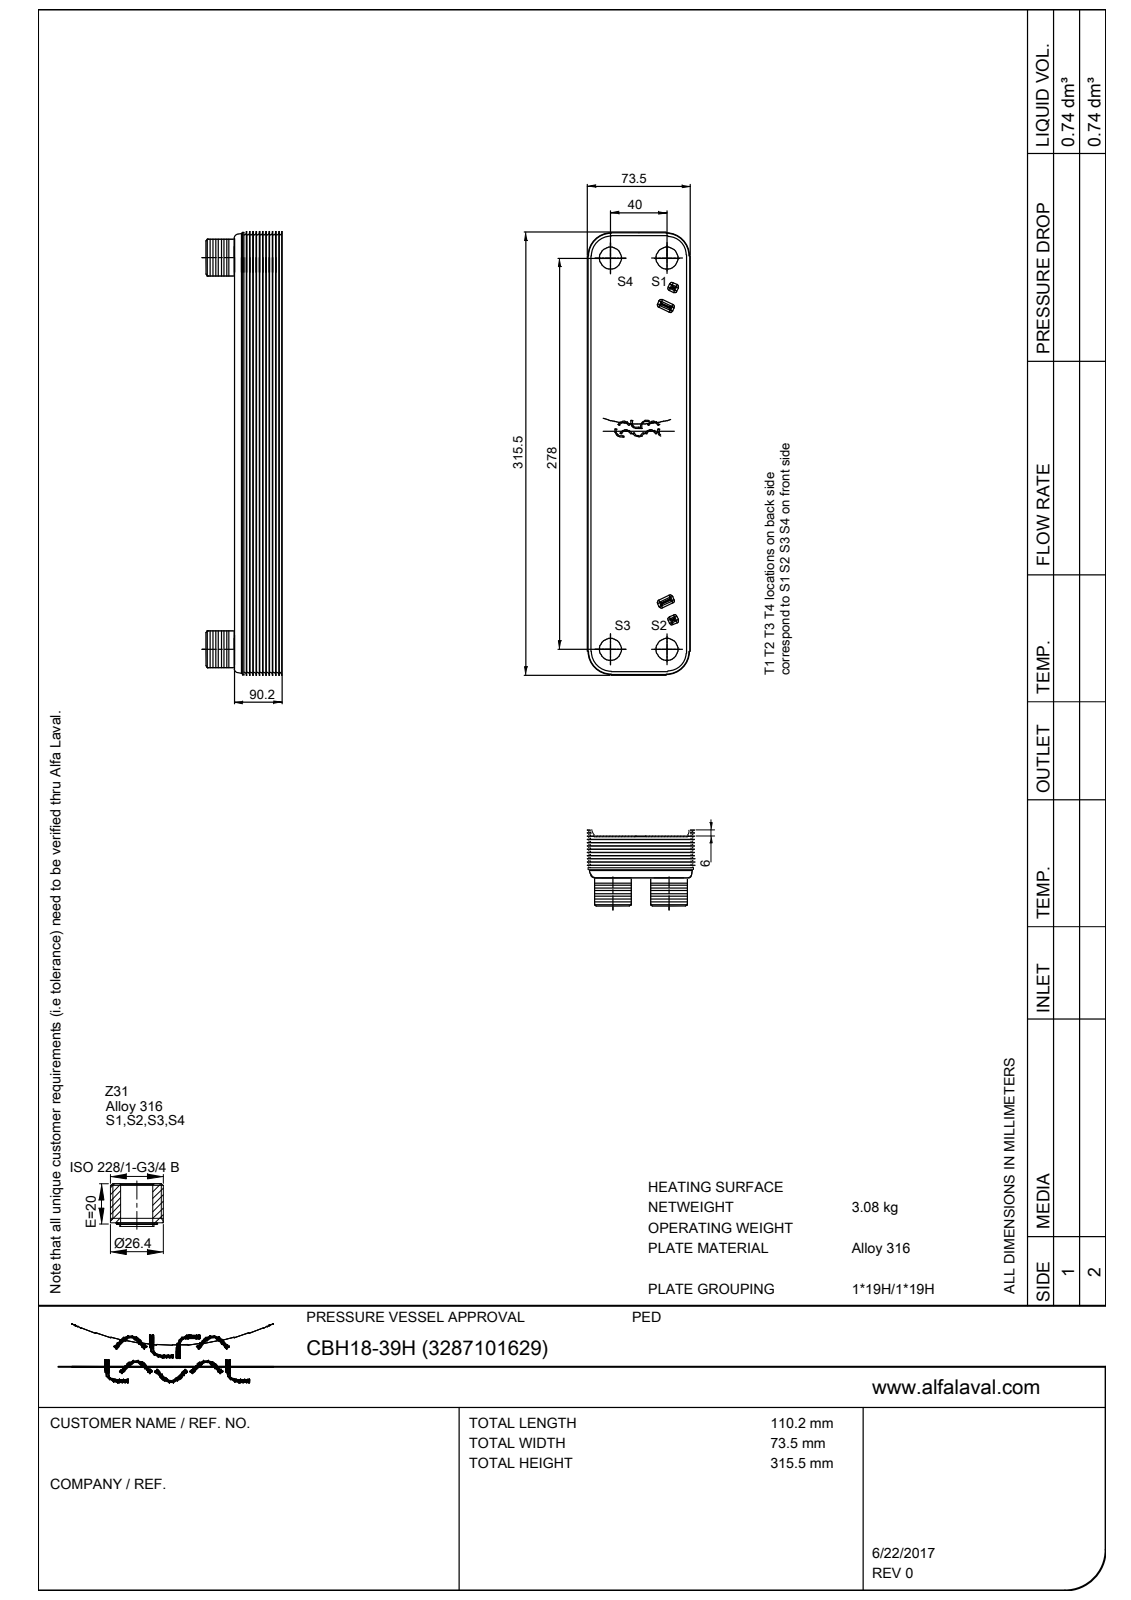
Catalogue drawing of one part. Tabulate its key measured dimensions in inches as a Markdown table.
| quantity | value |
| --- | --- |
| part name | CBH18_CH_39H; CBH18_FP_S1S2S3S4_16; CBH18_PP; Z31 (+1 more) |
| STEP written by | PRO/ENGINEER BY PARAMETRIC TECHNOLOGY CORPORATION, 2007390 (CONFIG_CONTROL_DESIGN) |
| units | inches |
| bodies | 7 solids, 480 faces (128 planar, 144 cylindrical, 208 other) |
| overall size | 12.559 × 4.417 × 3.051 |
| volume | 125.6 in³ |
| surface area | 395.4 in² |
| round holes (diameter × count) | 0.63 × 4, 0.659 × 4, 0.807 × 4 |
| round bosses / shafts (diameter × count) | 1.041 × 4, 0.709 × 4 |
| partial cylindrical surfaces (radius × count) | 0.039 × 18, 0.016 × 16, 0.028 × 16, 0.055 × 16, 0.067 × 16, 0.02 × 4, 0.059 × 4, 0.787 × 4 |
| main face-to-face distances | 0.039, 3.366, 3.327, 3.051, 3.406, 0.47, 0.041, 0.045, 3.411, 12.559 |
| hole center spacings | 1.575, 10.945, 11.057 |
